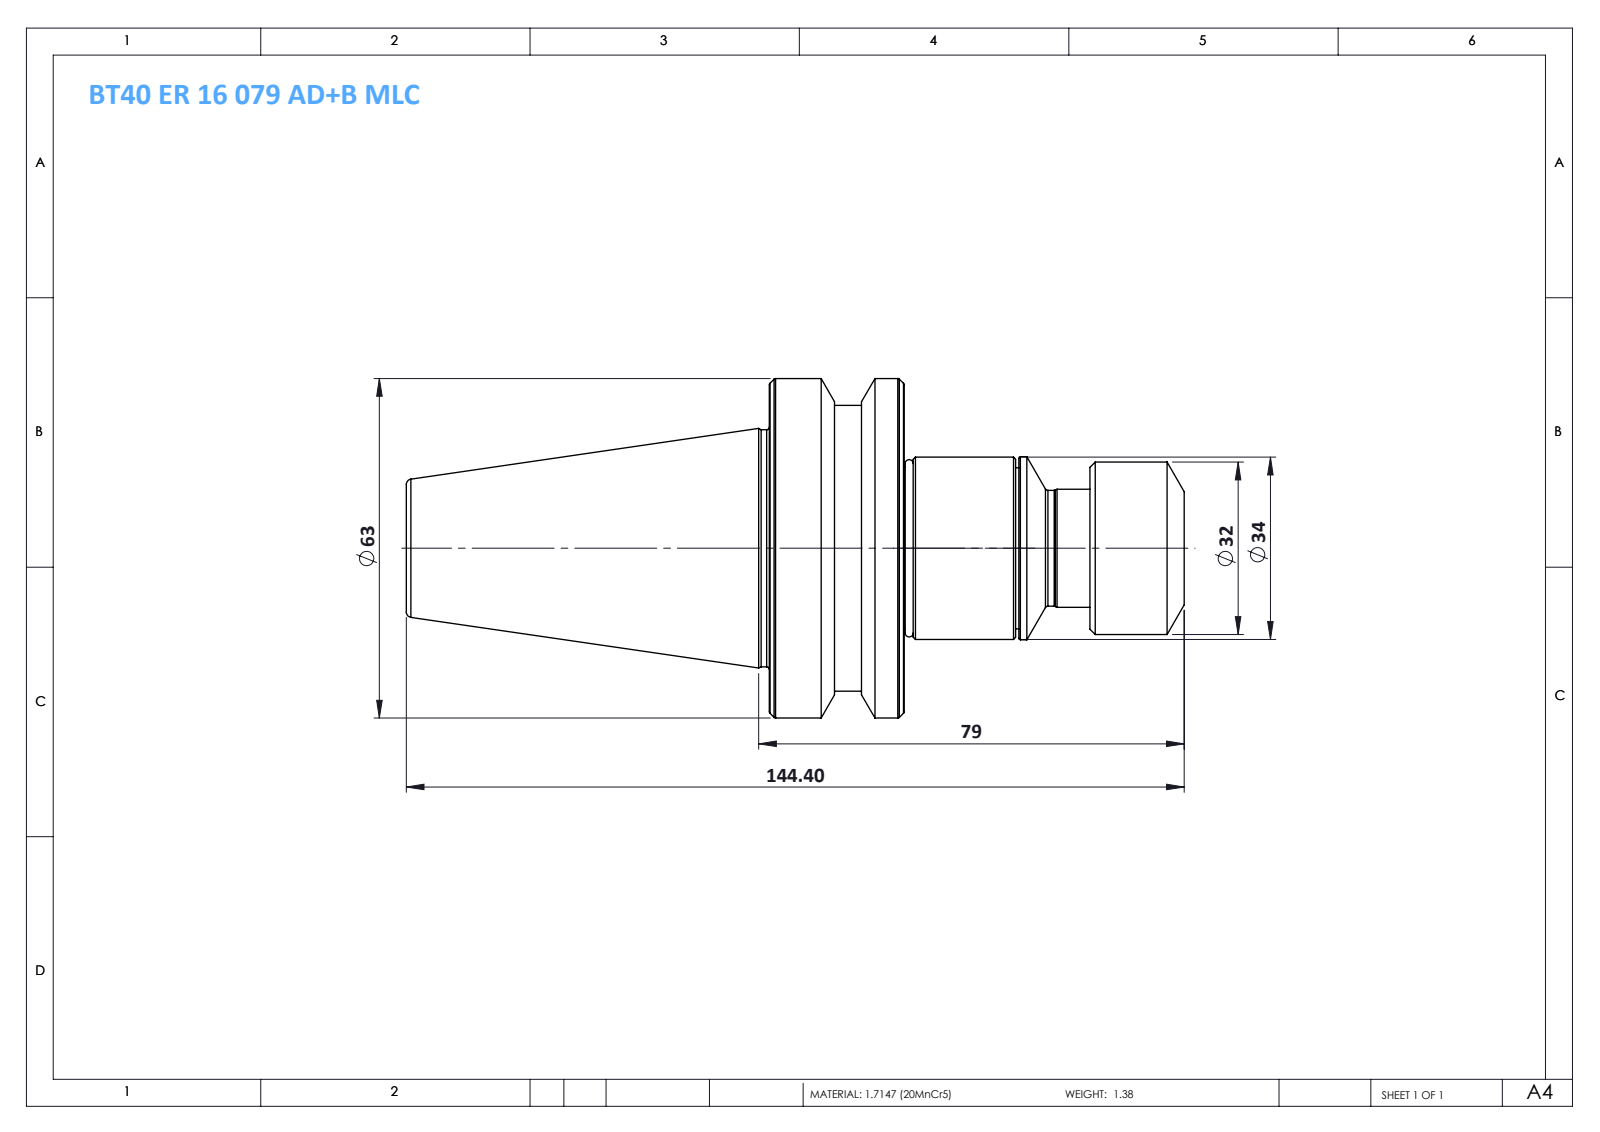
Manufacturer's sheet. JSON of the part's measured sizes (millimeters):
{"part_name": "BT40 ER 16 079 AD+B MLC", "step_written_by": "SolidWorks 2014 (CONFIG_CONTROL_DESIGN)", "units": "millimeters", "bodies": {"solids": 1, "faces": 77, "planar": 11, "cylindrical": 20, "other": 46}, "overall_size": [144.4, 63, 63], "volume_mm3": 177033, "surface_area_mm2": 24481, "round_bosses_or_shafts": [[63, 1], [53, 1], [44, 1], [34, 1], [33.8, 1], [32, 1], [29.9, 1], [21.9, 1]], "face_to_face_distances": [25, 92.4, 67.4, 52, 77, 144.4, 17.5, 34.5, 59.5, 126.9]}
